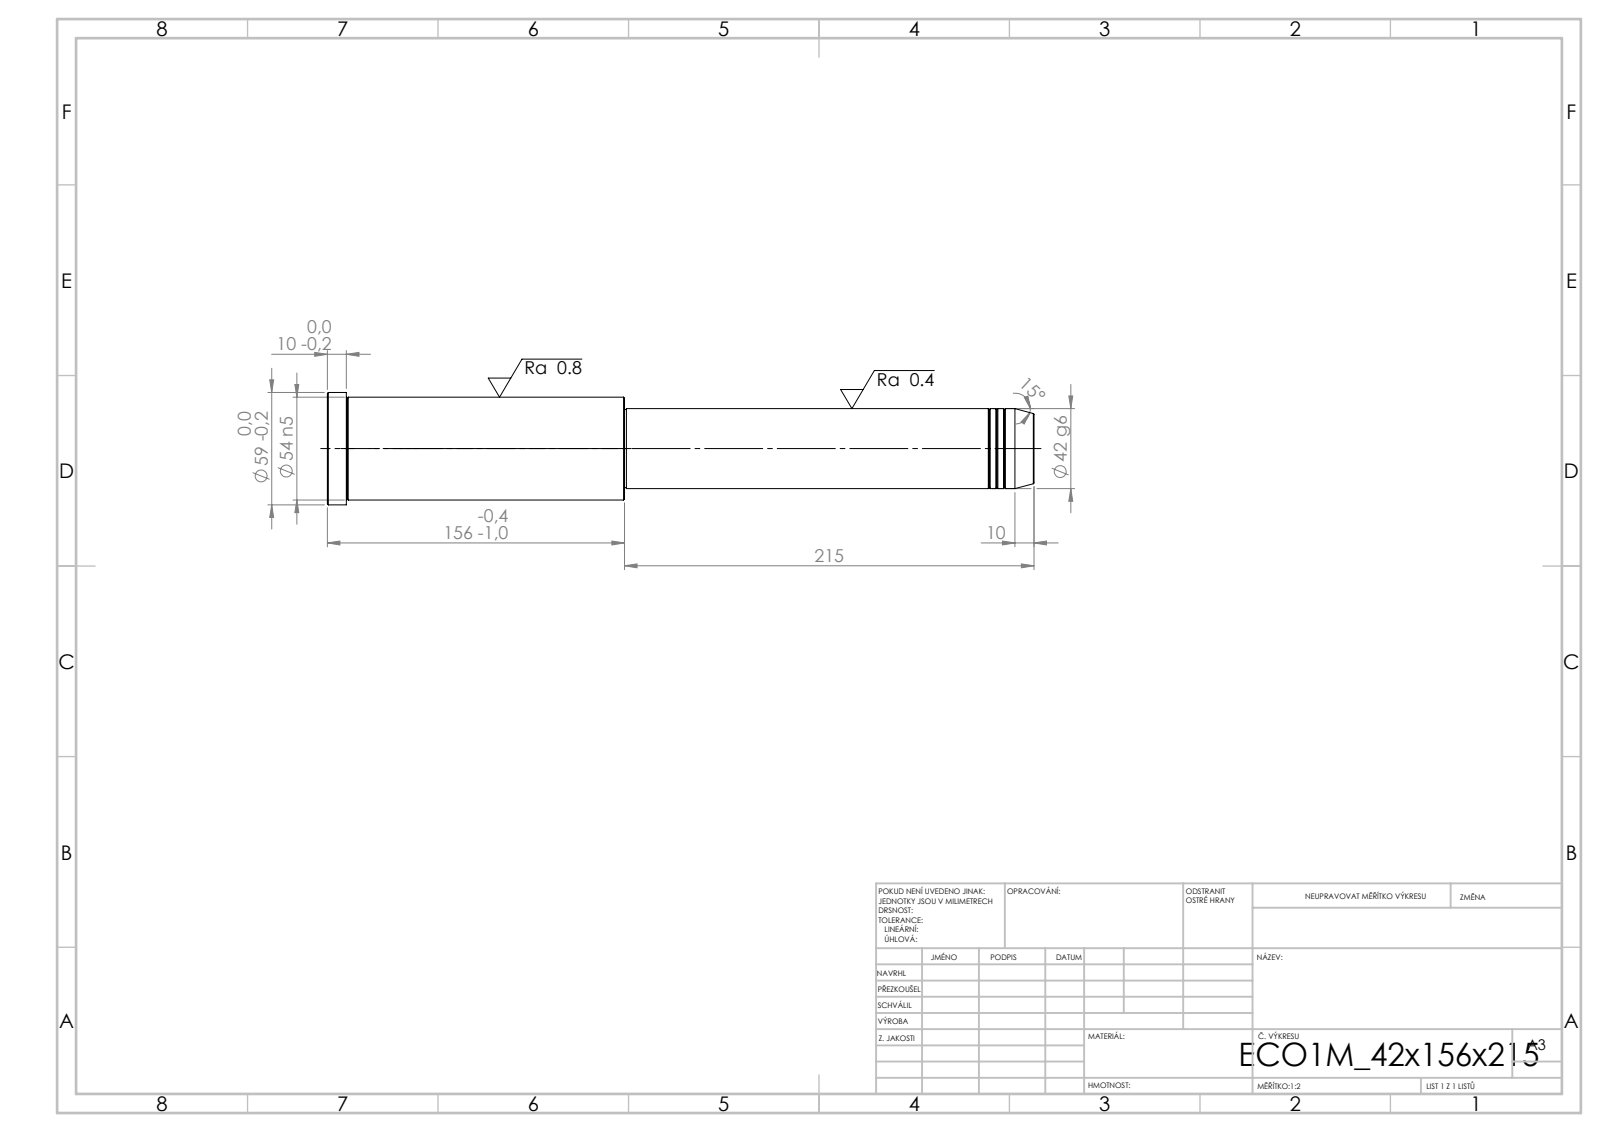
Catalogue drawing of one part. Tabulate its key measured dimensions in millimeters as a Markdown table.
| quantity | value |
| --- | --- |
| STEP written by | SolidWorks 2019 (CONFIG_CONTROL_DESIGN) |
| units | millimeters |
| bodies | 1 solid, 43 faces (5 planar, 14 cylindrical, 24 other) |
| overall size | 371 × 59 × 59 |
| volume | 657 557 mm³ |
| surface area | 60 407 mm² |
| round bosses / shafts (diameter × count) | 59 × 1, 54 × 1, 42 × 1, 41 × 1 |
| main face-to-face distances | 371, 215, 156, 361, 146, 10, 214, 1, 147, 157 |
